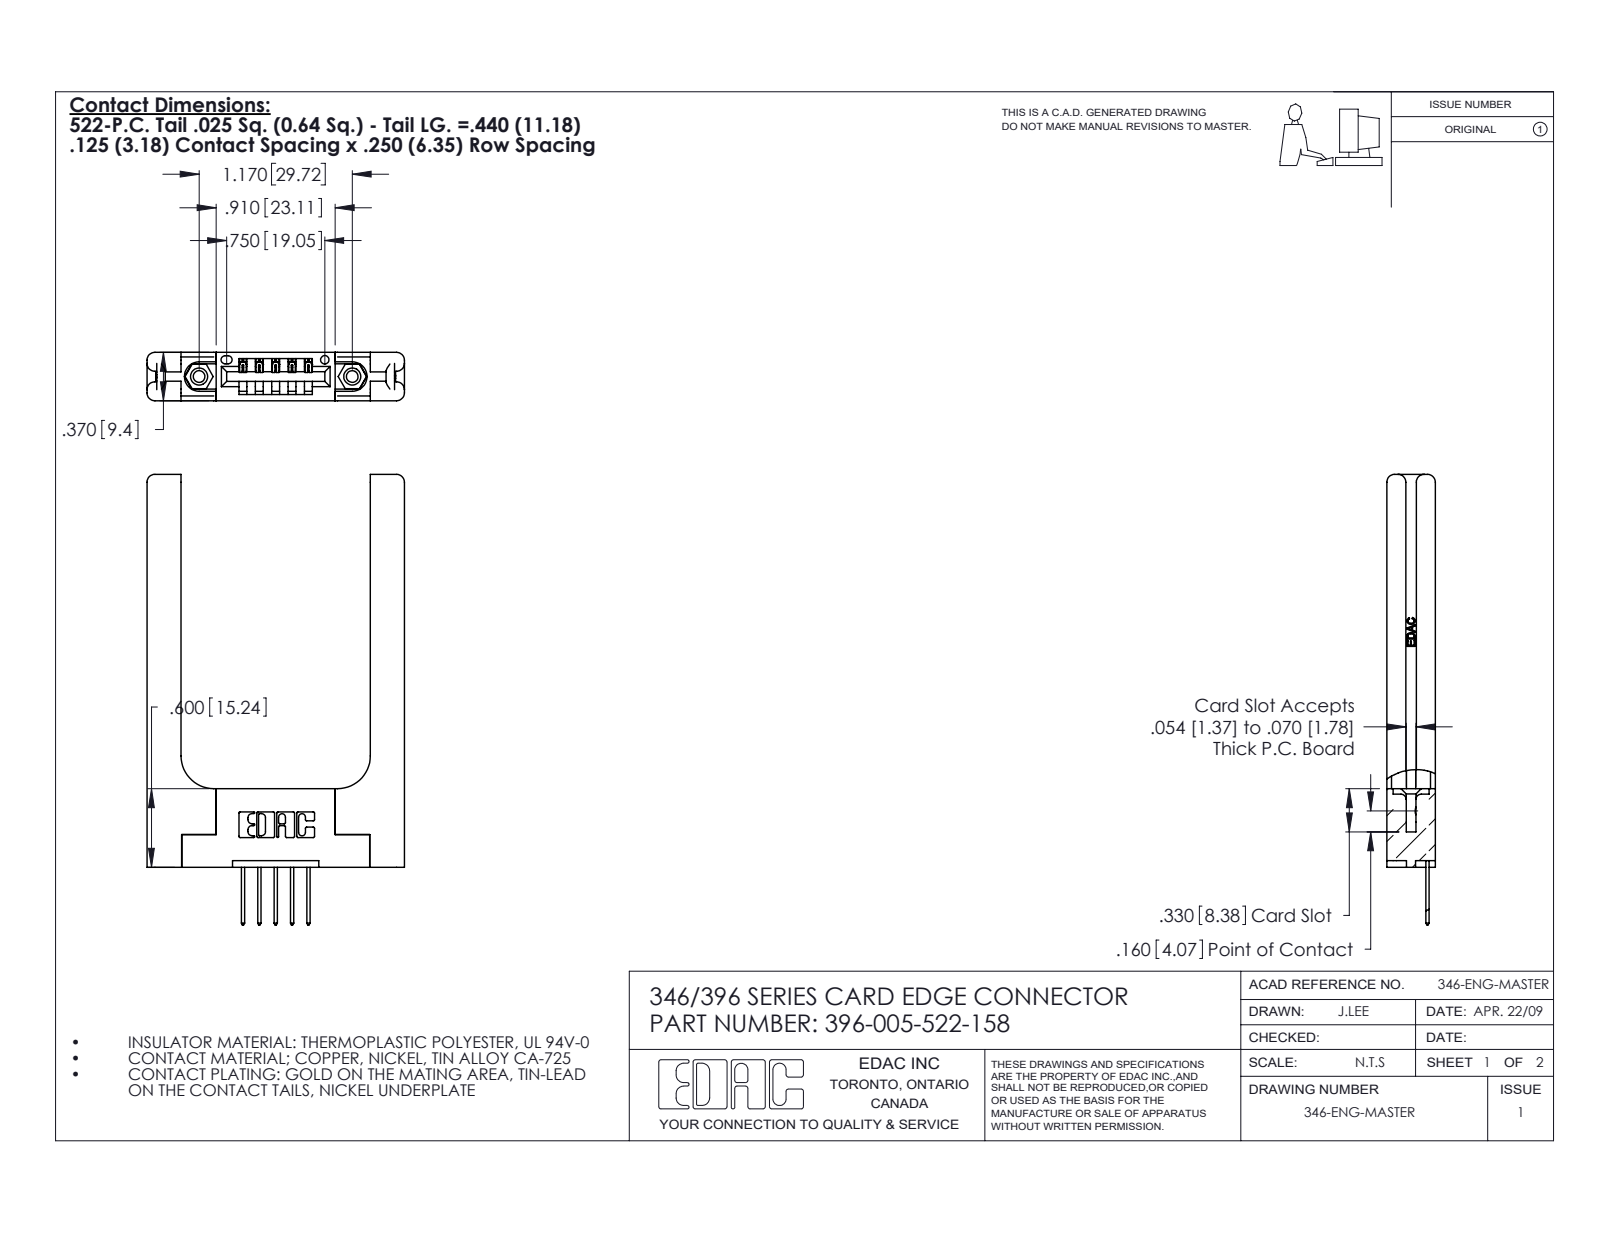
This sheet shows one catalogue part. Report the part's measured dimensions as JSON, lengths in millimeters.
{"part_name": "345-250-001_345-250-001-102; 396-005-522-158; 345-292-001_345-293-122; 346-220-058_345-220-058 (+1 more)", "step_written_by": "SolidWorks 2020 (CONFIG_CONTROL_DESIGN)", "units": "millimeters", "bodies": {"solids": 10, "faces": 682, "planar": 438, "cylindrical": 184, "other": 60}, "overall_size": [87.4, 49.9, 9.4], "volume_mm3": 12000, "surface_area_mm2": 10460, "round_holes": [[2.3, 2], [3.2, 2], [4, 2], [1.6, 1]], "round_bosses_or_shafts": [[3.9, 2]], "partial_cylinders_radius": [[0.3, 22], [1.5, 16], [0.2, 10], [0.3, 10], [0.2, 6], [0.8, 6], [0.7, 3], [0.8, 2]], "face_to_face_distances": [9.4, 3.8, 5.6, 1.8, 6.4, 36.7, 3.8, 1.8, 6.6, 43.3], "hole_center_spacings": [6.2, 24.6, 29.7]}
